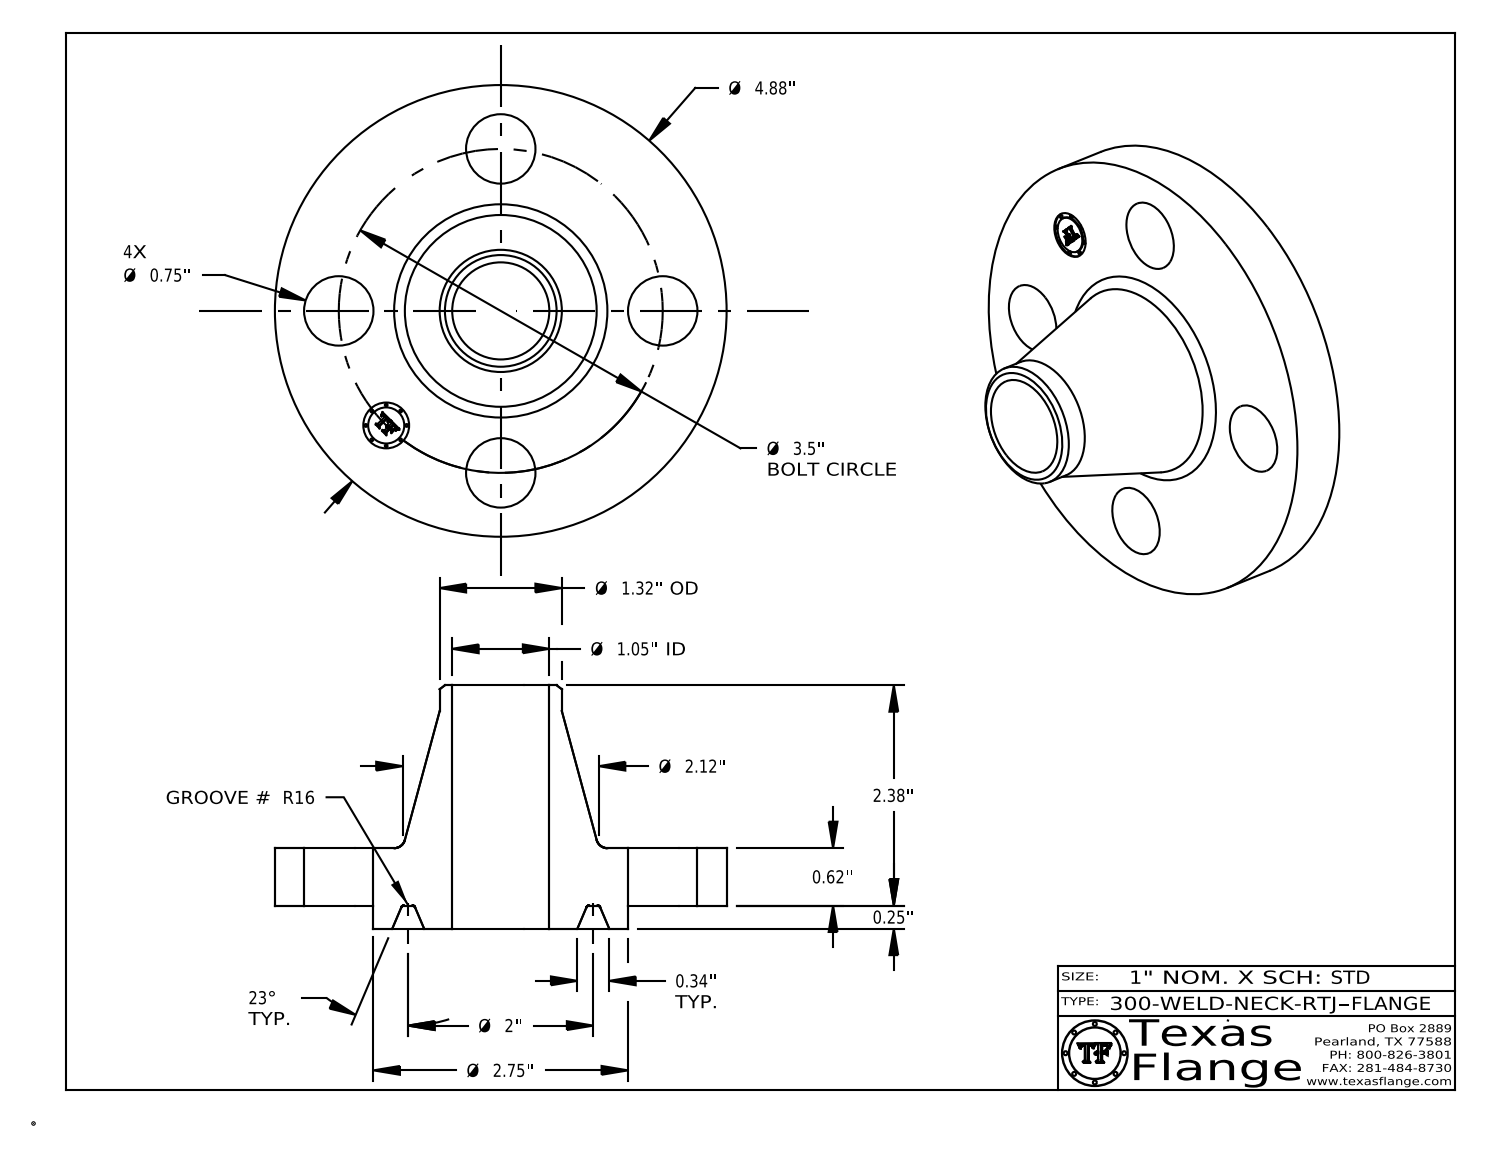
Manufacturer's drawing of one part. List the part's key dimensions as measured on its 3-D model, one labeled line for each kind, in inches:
Part name (STEP PRODUCT): 300-WELD-NECK-RTJ
STEP written by: CATIA V5 STEP AP214 (AUTOMOTIVE_DESIGN)
Units: inches
Bodies: 1 solid, 421 faces (371 planar, 36 cylindrical, 14 other)
Overall size (bounding box): 4.88 × 4.88 × 2.63
Volume: 13.23 in³ · Surface area: 67.42 in²
Round holes (diameter × count): ⌀0.75 ×4, ⌀0.495 ×1, ⌀1.049 ×1
Round bosses / shafts (diameter × count): ⌀0.03 ×8, ⌀4.88 ×1, ⌀2.75 ×1, ⌀1.32 ×1, ⌀0.39 ×1
Main face-to-face distances: 0.62, 0.25, 0.87, 2.63, 2.38, 1.76, 0.015, 0.855, 0.605, 1.775
Hole centre spacings: 1.75, 2.475, 1.339, 3.233, 3.5
